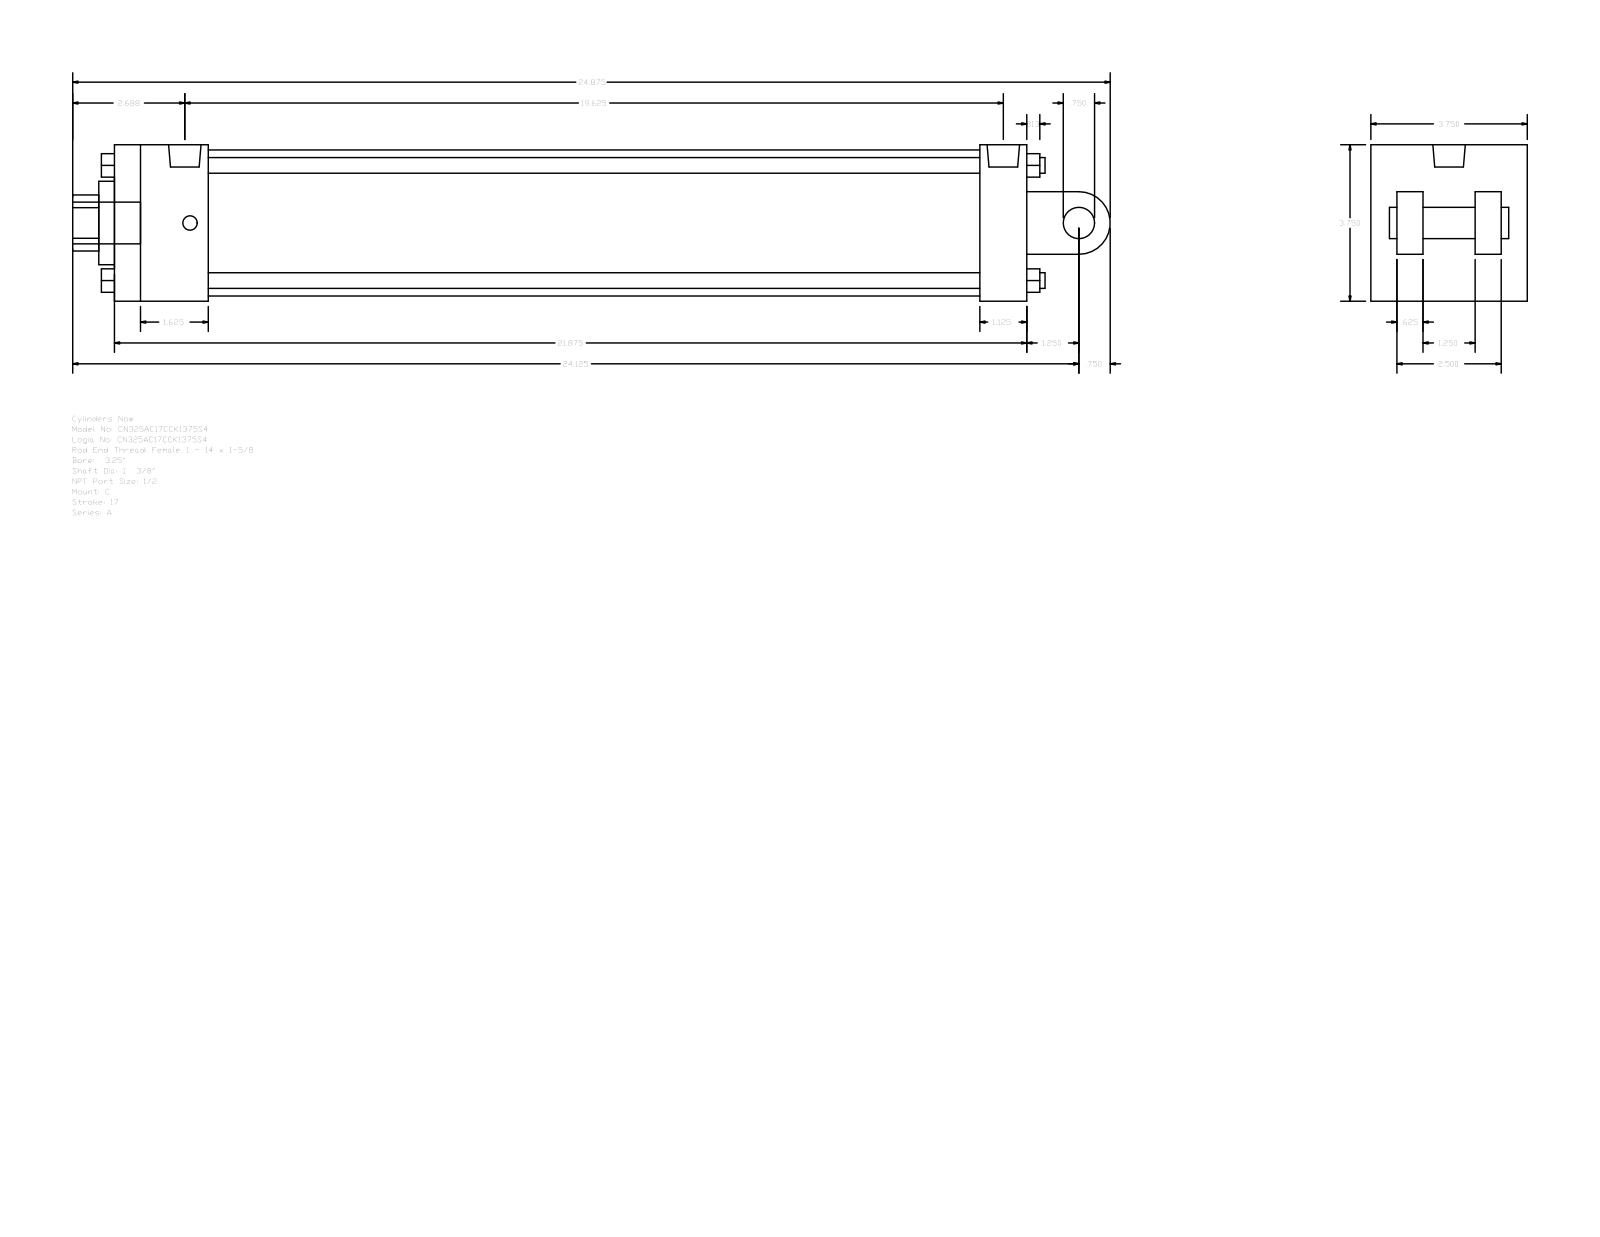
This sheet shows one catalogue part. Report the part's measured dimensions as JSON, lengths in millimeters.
{"part_name": "A_C__0325_1.375", "step_written_by": "GSSL Pune (CONFIG_CONTROL_DESIGN)", "units": "millimeters", "bodies": {"solids": 0, "faces": 135, "planar": 102, "cylindrical": 33, "other": 0}, "overall_size": [631.83, 95.25, 95.25], "round_holes": [[8.73, 2], [19.77, 1], [34.92, 1], [50.8, 1], [88.9, 1]], "round_bosses_or_shafts": [[9.53, 4], [8.73, 2], [25.4, 1], [19.77, 1], [19.05, 1]], "partial_cylinders_radius": [[17.06, 1], [19.05, 1]], "face_to_face_distances": [95.24, 15.87, 555.62, 28.57, 63.5, 66.67, 31.74, 79.37, 47.63, 527.05], "hole_center_spacings": [3.18]}
